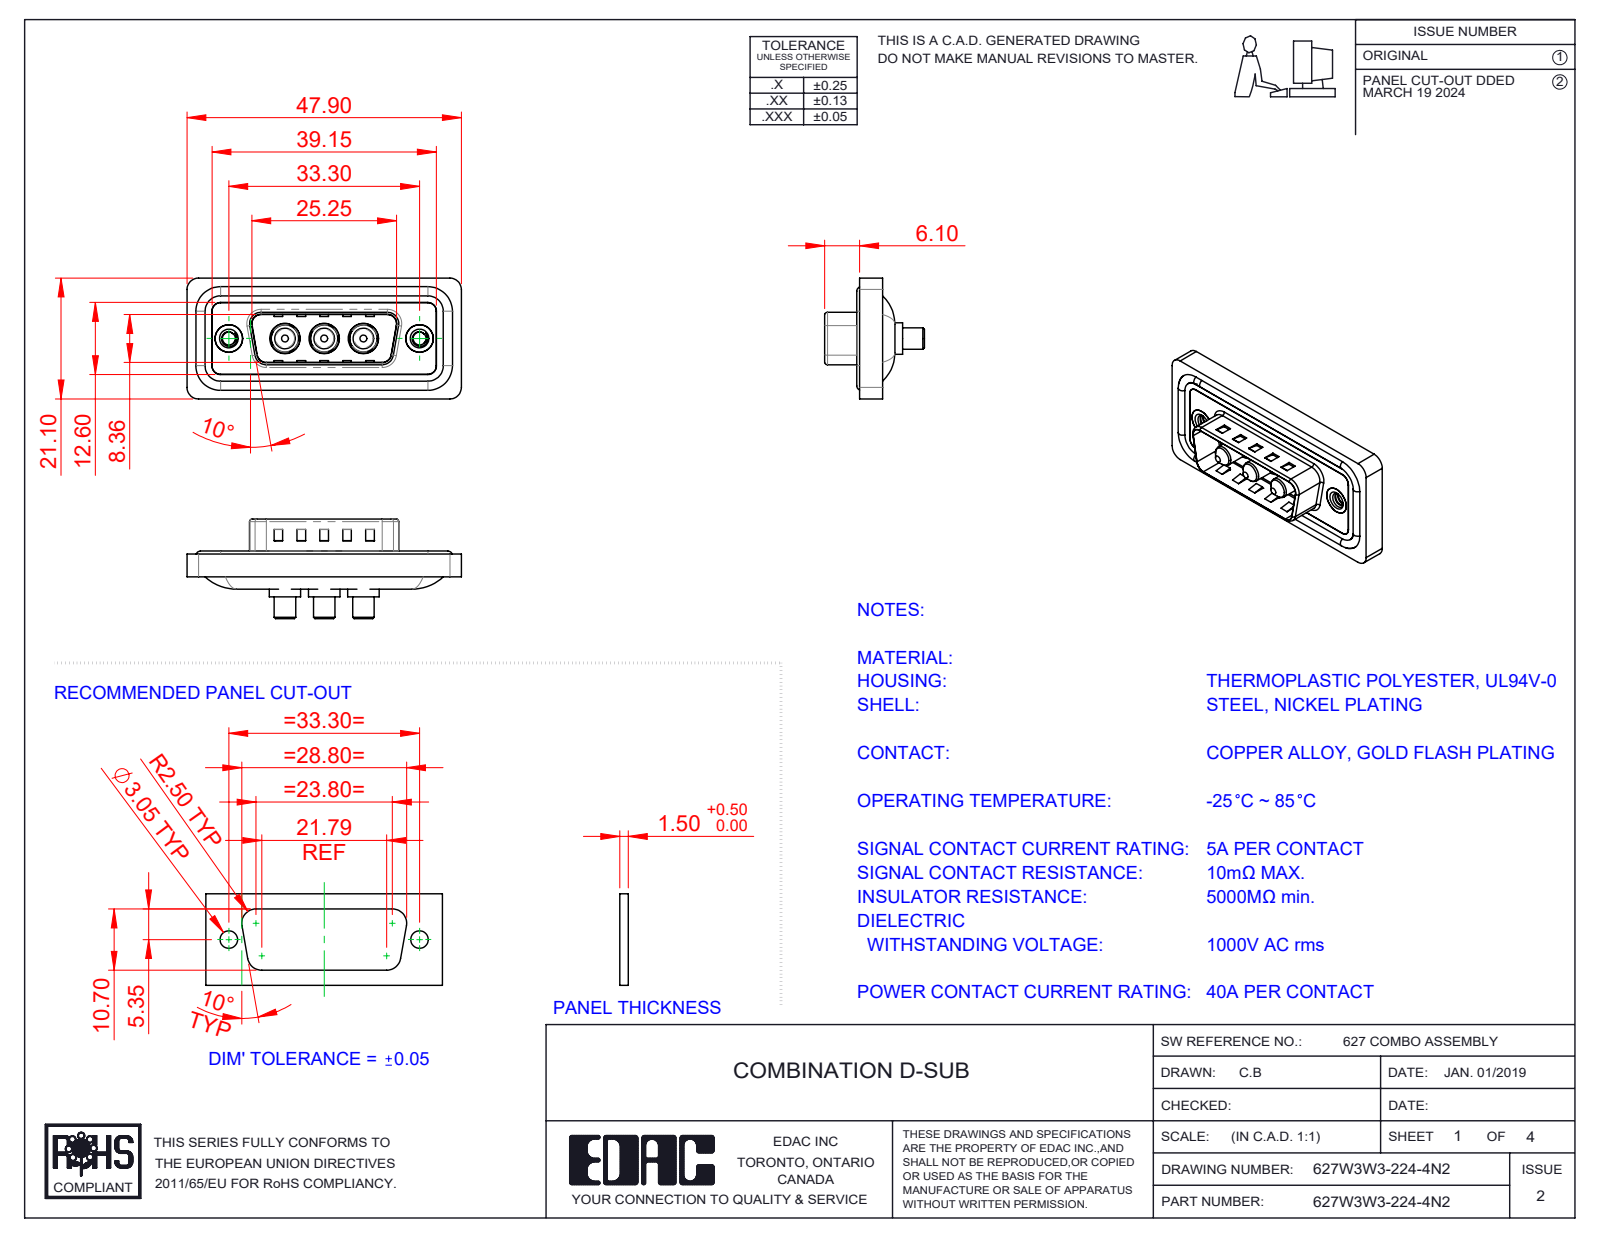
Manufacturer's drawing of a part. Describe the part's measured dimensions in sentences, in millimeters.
The part is named "627Combo Shell Rear_15 Contacts; 627Combo Housing_3W3; 627Combo Waterproof Housing_15 Contacts; 627Combo Shell Front_15 Contacts (+3 more)". Its 3-D file was written by "SolidWorks 2023 (CONFIG_CONTROL_DESIGN)". It is 13 solids with 564 faces: 207 planar, 241 cylindrical and 116 other. Overall it measures 47.9 by 21.1 by 17.4 millimeters. Its volume is 5 641 cubic millimeters and its surface area 8 786 square millimeters. Round holes: 3 of diameter 4.85, 3 of diameter 5.3, 2 of diameter 2.26, 2 of diameter 4, 2 of diameter 4.8, 2 of diameter 5. Round bosses or shafts: 4 of diameter 1.6, 3 of diameter 5.5, 3 of diameter 5.2, 3 of diameter 4.75, 3 of diameter 3.75, 3 of diameter 3.6, 2 of diameter 4.9. Partial cylindrical surfaces (rounded edges, fillets, slot ends): 26 of radius 1.5, 20 of radius 2, 8 of radius 0.5, 8 of radius 1.6, 4 of radius 0.25, 4 of radius 0.6, 4 of radius 0.65, 4 of radius 0.9. The main face-to-face distances are 0.4, 1.1, 1.5, 0.5, 1.6, 3.1, 2.9, 4, 0.82, 9.58. The hole center spacings are 6.85, 9.8, 16.65, 23.5, 13.7, 33.3.
